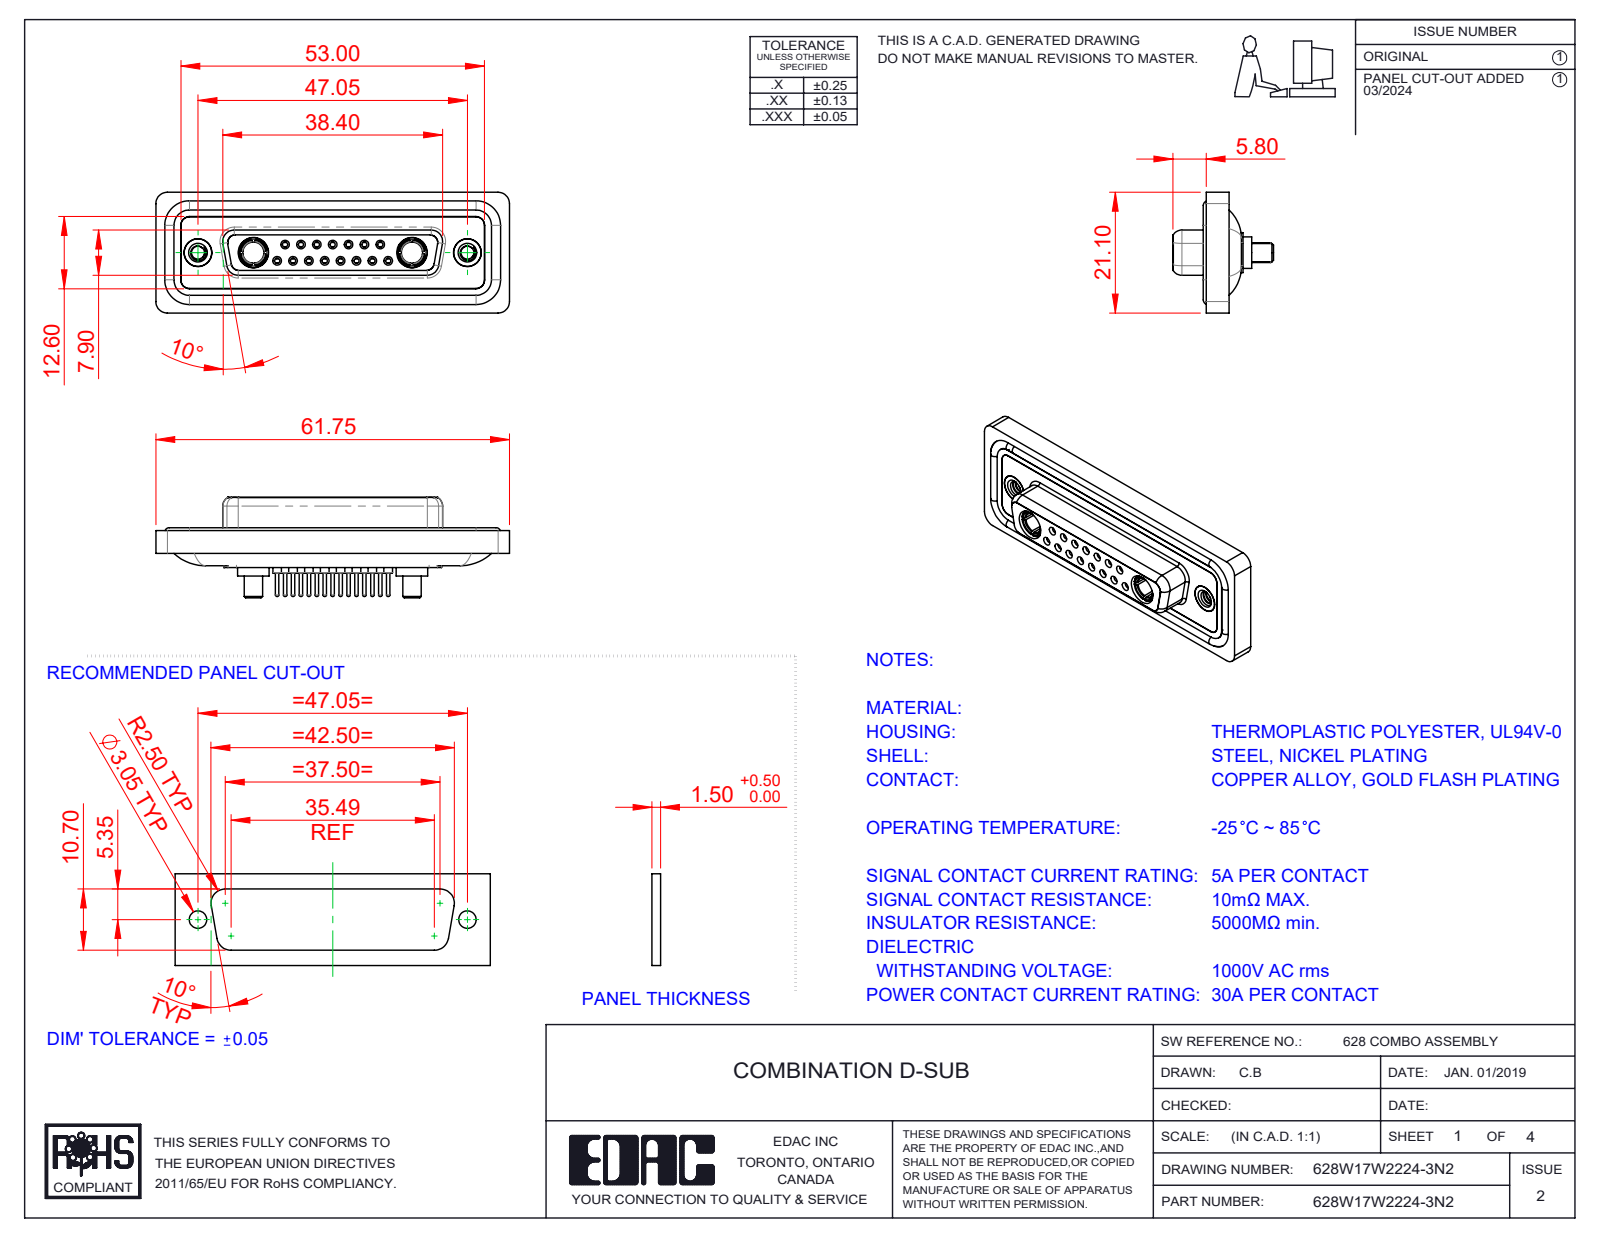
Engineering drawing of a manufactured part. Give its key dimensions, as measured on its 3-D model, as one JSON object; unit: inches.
{"part_name": "628Combo Shell Front_25 Contacts; 628Combo Contact Row 2_24; 628Combo Threaded Rivet_2; Power Socket_30A S (+5 more)", "step_written_by": "SolidWorks 2023 (CONFIG_CONTROL_DESIGN)", "units": "inches", "bodies": {"solids": 26, "faces": 1359, "planar": 388, "cylindrical": 519, "other": 452}, "overall_size": [2.431, 0.831, 0.691], "volume_in3": 0.509, "surface_area_in2": 21.49, "round_holes": [[0.035, 15], [0.043, 15], [0.059, 15], [0.079, 15], [0.063, 8], [0.067, 7], [0.191, 4], [0.089, 2], [0.146, 2], [0.157, 2], [0.159, 2], [0.197, 2]], "round_bosses_or_shafts": [[0.087, 15], [0.024, 15], [0.063, 11], [0.217, 2], [0.205, 2], [0.195, 2], [0.195, 2], [0.189, 2]], "partial_cylinders_radius": [[0.059, 22], [0.079, 18], [0.053, 8], [0.063, 8], [0.01, 4], [0.02, 4], [0.024, 4], [0.026, 4]], "face_to_face_distances": [0.016, 0.071, 0.293, 0.222, 0.26, 0.02, 0.278, 0.063, 0.114, 0.043], "hole_center_spacings": [0.124, 0.109, 0.327, 0.218, 0.198, 0.198, 0.295, 0.436]}
